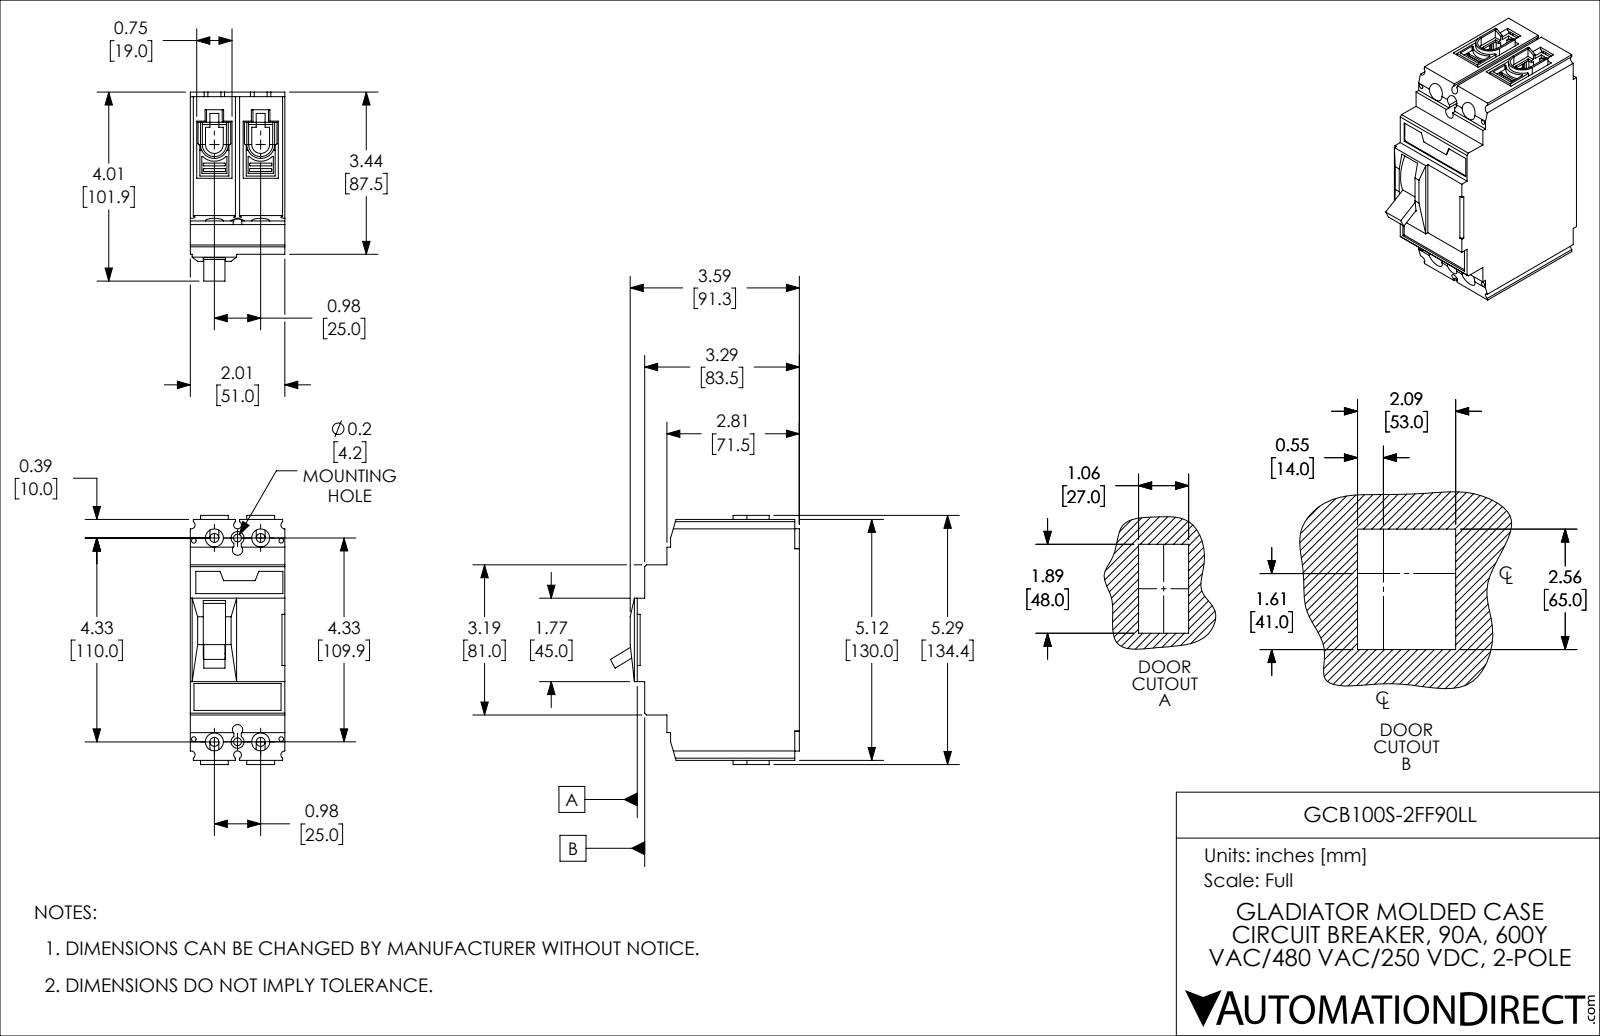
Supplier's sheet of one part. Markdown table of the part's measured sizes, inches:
| quantity | value |
| --- | --- |
| part name | GCB100S-2FF90LL |
| STEP written by | SolidWorks 2021 (CONFIG_CONTROL_DESIGN) |
| units | inches |
| bodies | 1 solid, 839 faces (529 planar, 278 cylindrical, 32 other) |
| overall size | 5.291 × 4.013 × 2.008 |
| volume | 29.1 in³ |
| surface area | 110.4 in² |
| round holes (diameter × count) | 0.098 × 4, 0.165 × 4, 0.189 × 4, 0.382 × 4, 0.276 × 2 |
| partial cylindrical surfaces (radius × count) | 0.012 × 58, 0.02 × 26, 0.039 × 10, 0.157 × 10, 0.024 × 4, 0.083 × 4, 0.11 × 2, 0.189 × 2 |
| main face-to-face distances | 2.008, 0.984, 0.622, 4.496, 0.748, 1.87, 0.11, 0.886, 1.122, 0.138 |
| hole center spacings | 0.441, 0.492, 0.564, 0.931, 0.987, 1.422, 4.294, 4.357 |
